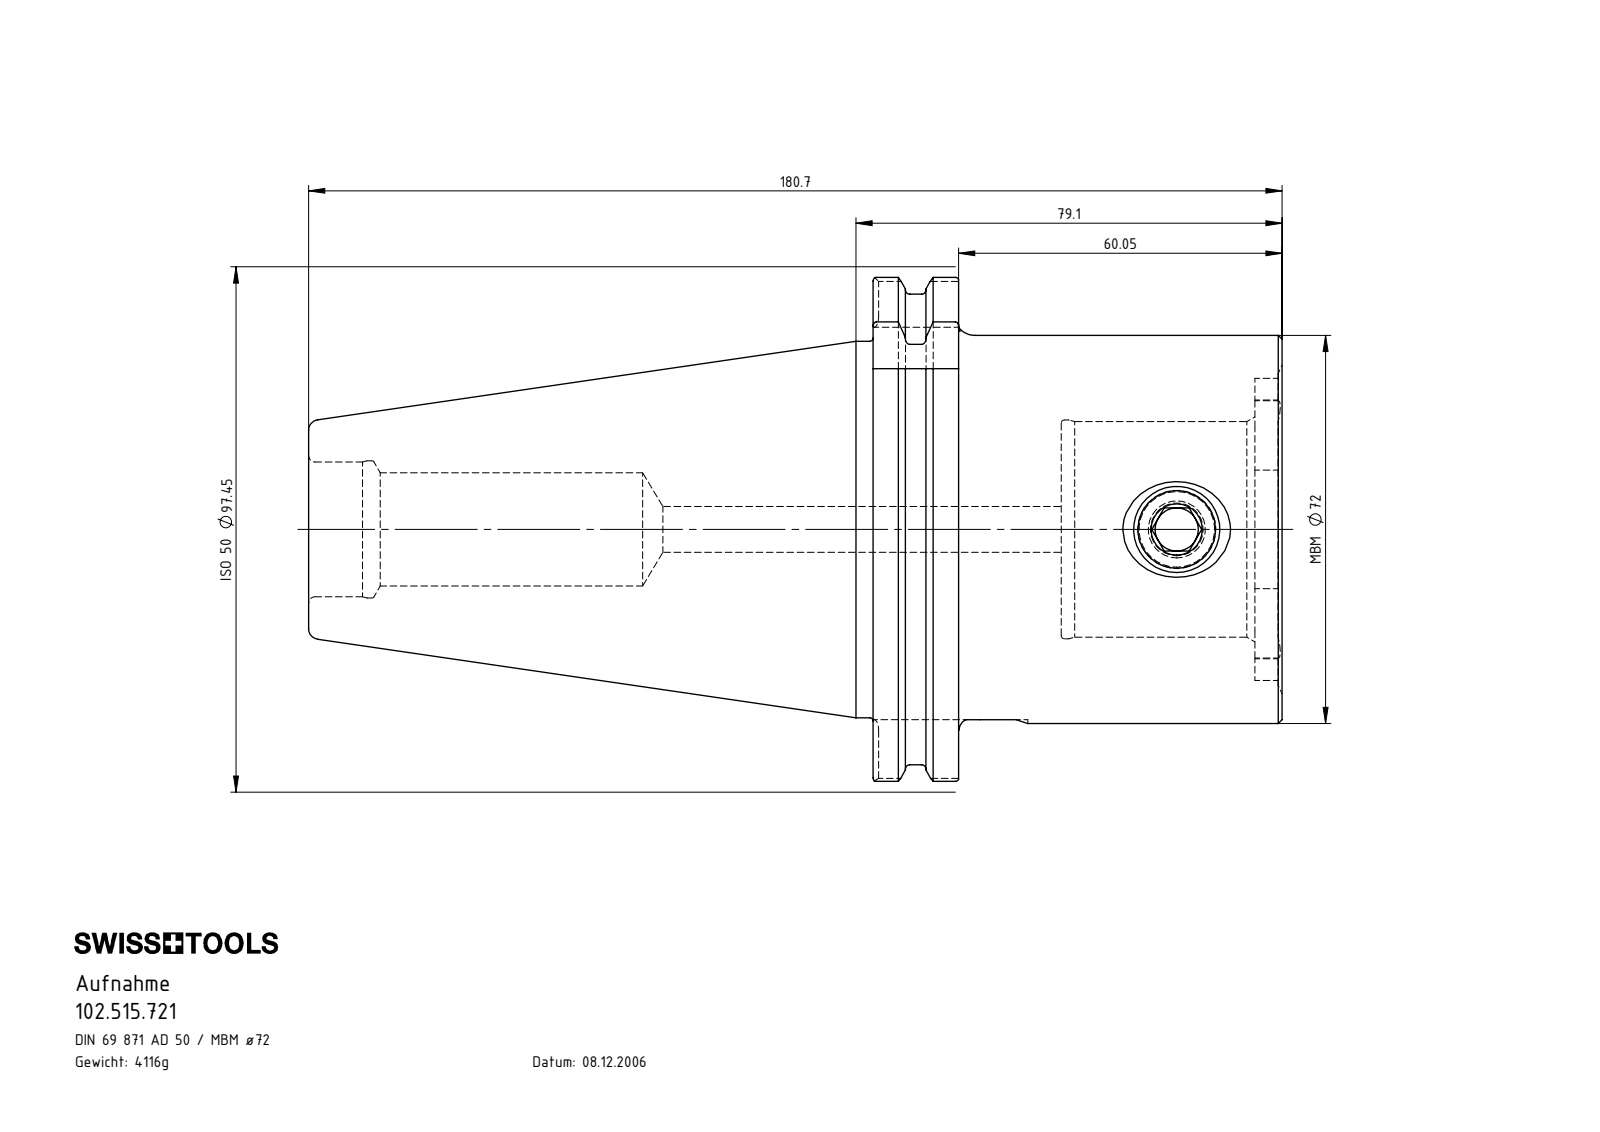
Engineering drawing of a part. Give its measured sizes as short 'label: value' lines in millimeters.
name: MB7-ER1.001.022_A; 102.515.721; SK5-MB7.K01.079_C
written by: SolidWorks 2017 (CONFIG_CONTROL_DESIGN)
unit: mm
bodies: 2 solids, 174 faces (56 planar, 51 cylindrical, 67 other)
size: 180.7 × 97.45 × 93.51
volume: 524 279 mm³; area: 61 875 mm²
holes: 1× ⌀8, 1× ⌀8.5, 1× ⌀14.5, 1× ⌀21, 1× ⌀25, 1× ⌀25.45, 1× ⌀40, 1× ⌀40.6
bosses: 1× ⌀91, 1× ⌀72, 1× ⌀69.85, 1× ⌀16
rounds: 8× R2, 4× R5.2, 1× R12.85, 1× R23.75, 1× R28.02, 1× R48.73
face distances: 15.85, 34.9, 19.05, 75.9, 60.05, 41, 70.85, 55, 35.95, 5.05
